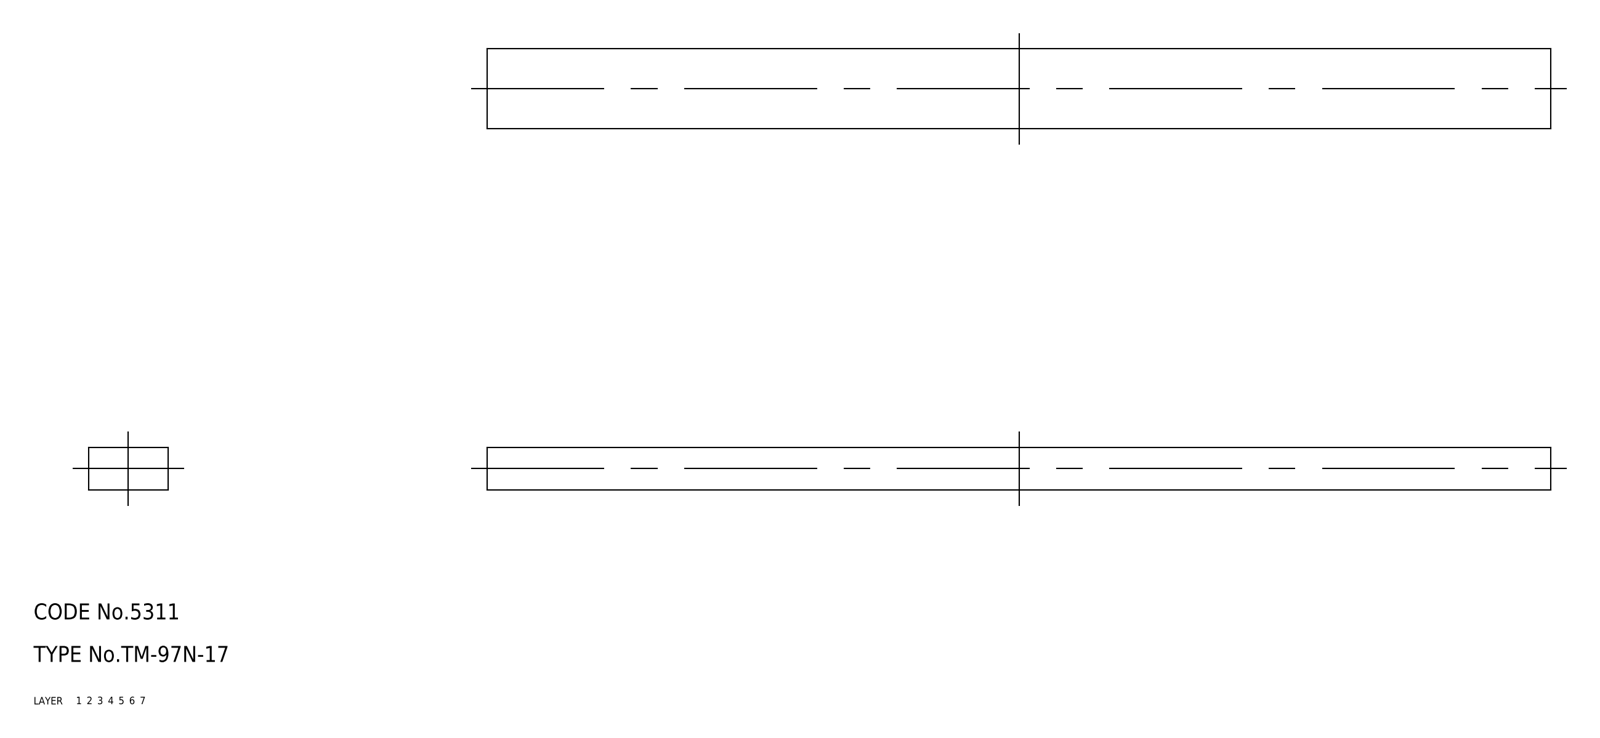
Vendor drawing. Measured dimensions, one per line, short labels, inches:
name: rubber foam
written by: CADfix (AUTOMOTIVE_DESIGN)
unit: in
bodies: 1 solid, 6 faces (0 planar, 0 cylindrical, 6 other)
size: 7.874 × 0.591 × 0.315
volume: 1.465 in³; area: 14.63 in²
